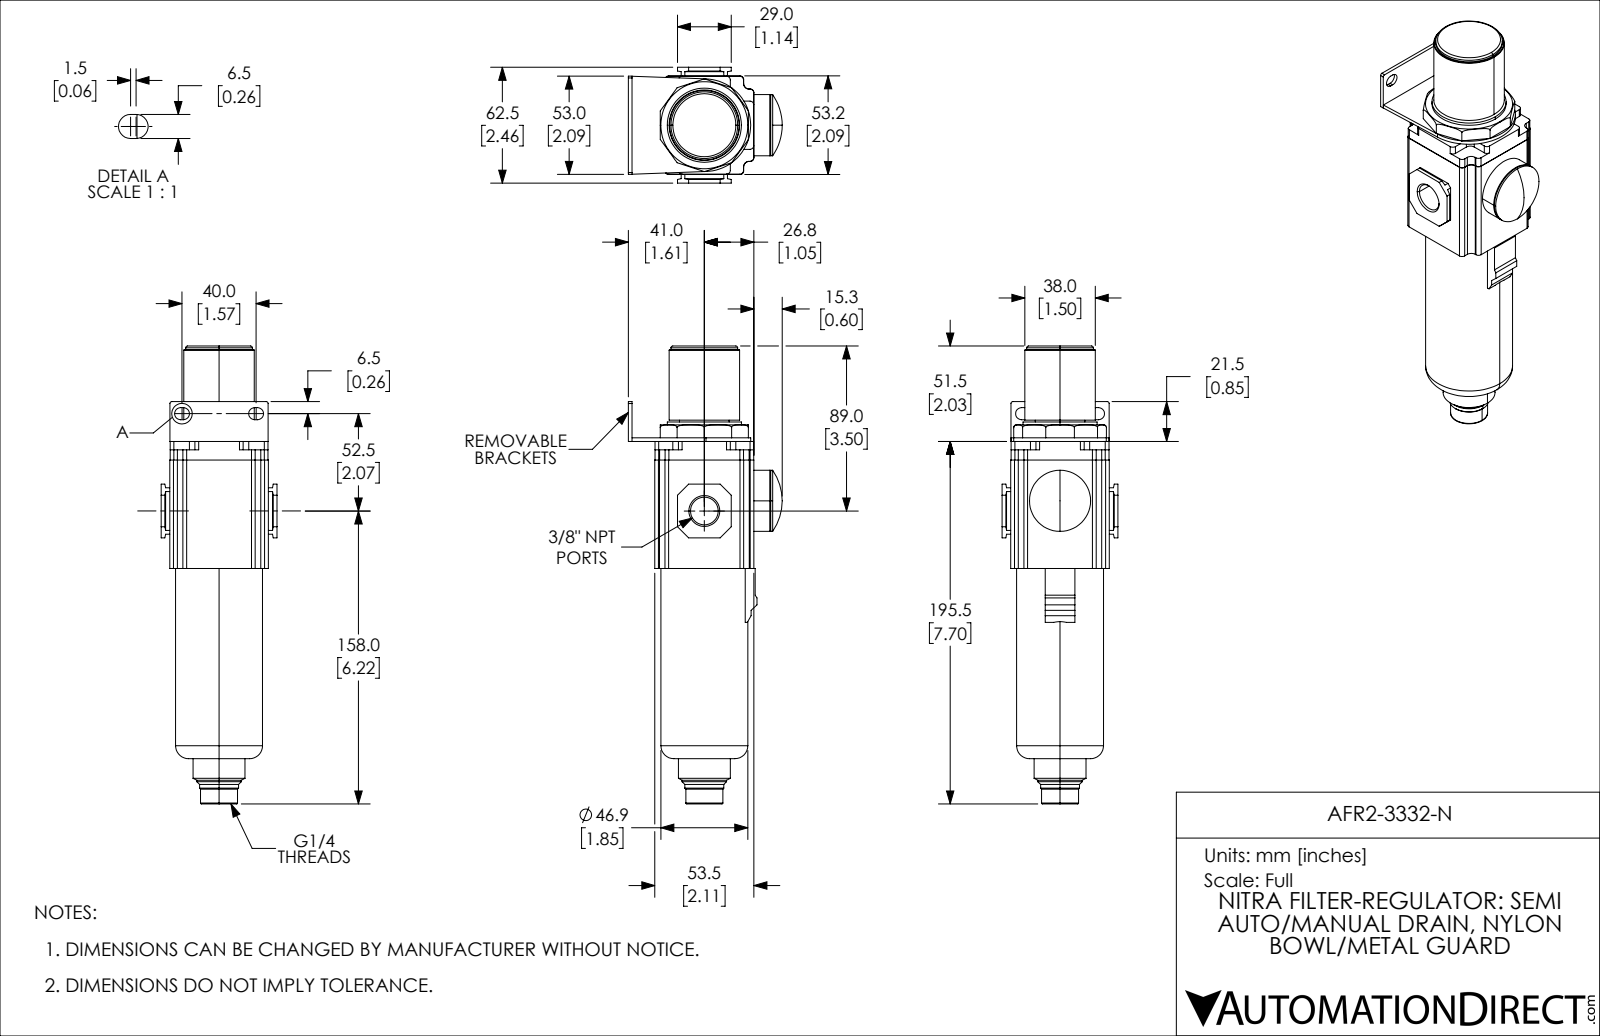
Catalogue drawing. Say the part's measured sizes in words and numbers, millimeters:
The part is named "AFR2-3332-N". Its 3-D file was written by "SolidWorks 2019 (CONFIG_CONTROL_DESIGN)". It is 1 solid with 221 faces: 124 planar, 71 cylindrical and 26 other. Overall it measures 247 by 83.03 by 62.5 millimeters. Its volume is 449 570 cubic millimeters and its surface area 52 239 square millimeters. Round holes: 1 of diameter 11.45, 1 of diameter 14.95. Round bosses or shafts: 1 of diameter 46.9, 1 of diameter 40, 1 of diameter 38, 1 of diameter 36, 1 of diameter 33, 1 of diameter 28, 1 of diameter 26.78, 1 of diameter 24. Partial cylindrical surfaces (rounded edges, fillets, slot ends): 24 of radius 2, 12 of radius 3, 4 of radius 3.25, 2 of radius 1, 1 of radius 25. The main face-to-face distances are 2, 53.2, 53.5, 14.25, 4.65, 57.85, 12.25, 67.75, 51.5, 49.5.
